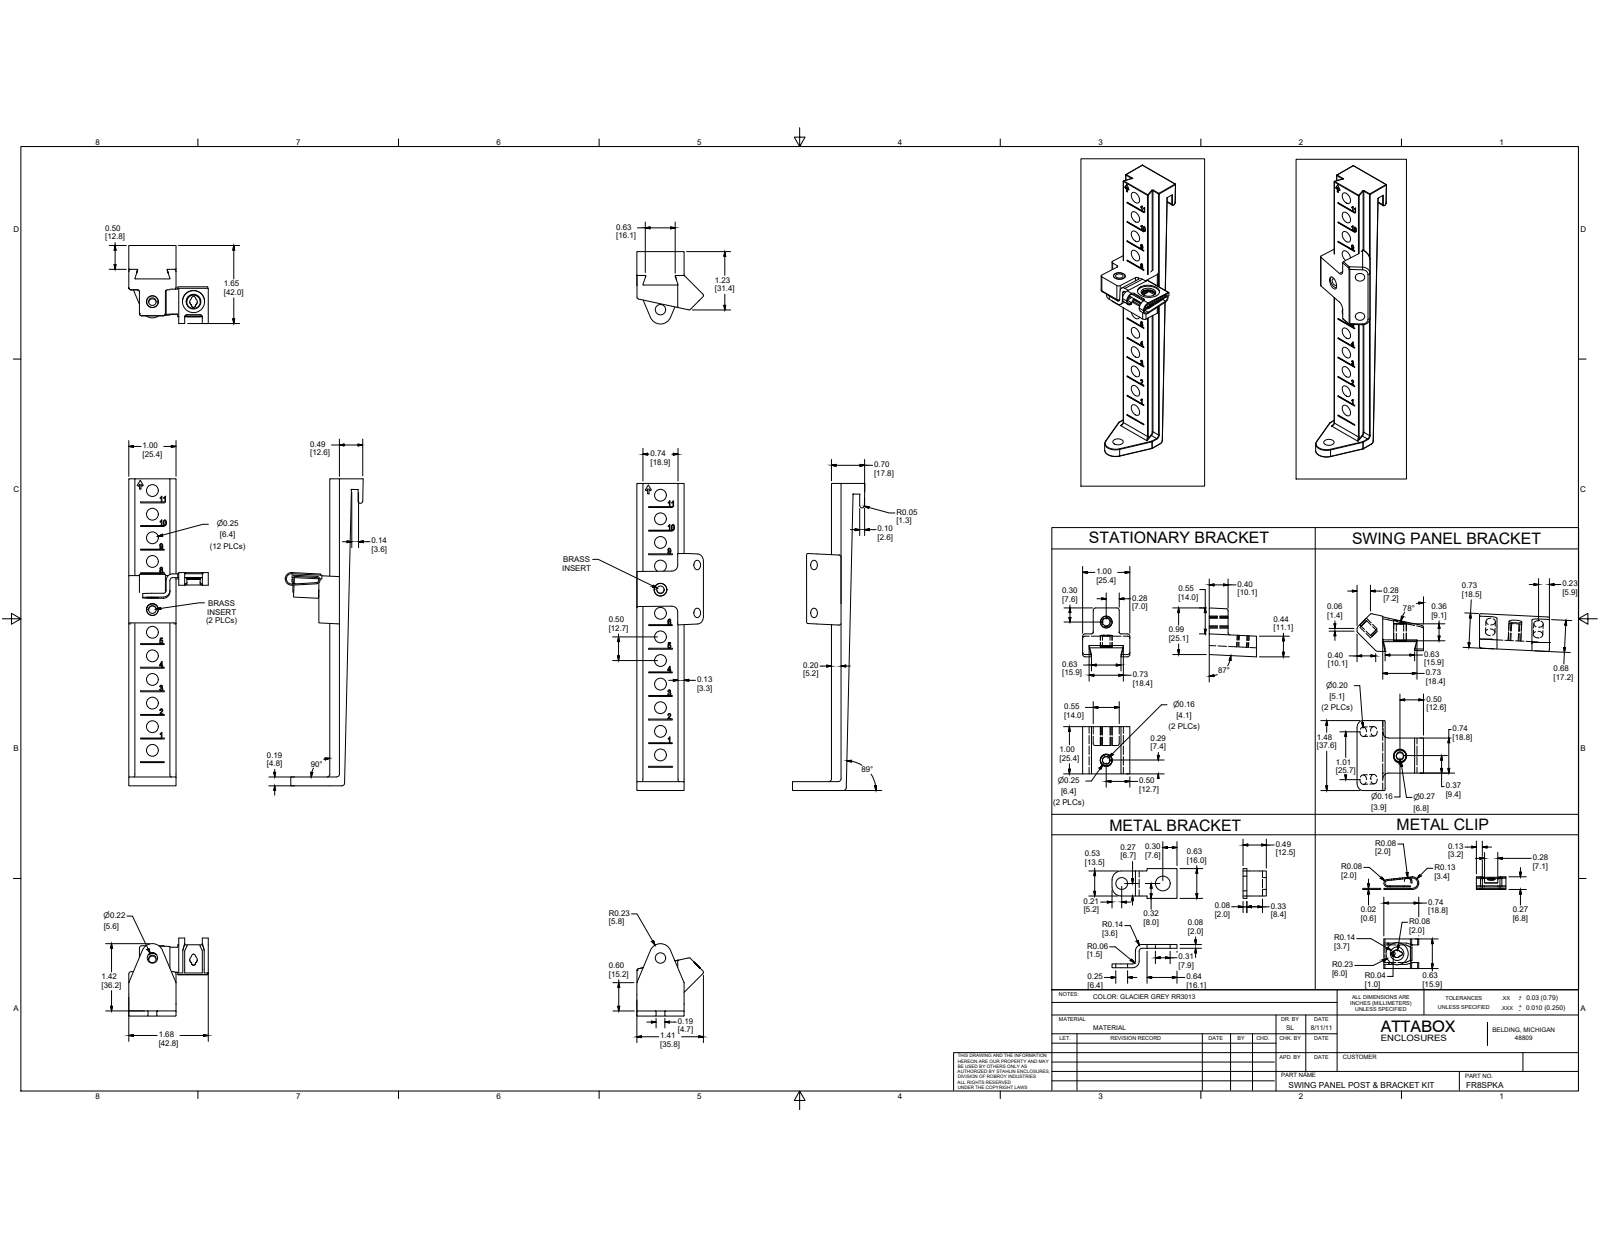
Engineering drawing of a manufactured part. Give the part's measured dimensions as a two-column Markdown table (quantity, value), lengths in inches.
| quantity | value |
| --- | --- |
| part name | FR8SPKA |
| STEP written by | SolidWorks 2019 (AUTOMOTIVE_DESIGN) |
| units | inches |
| bodies | 32 solids, 1984 faces (976 planar, 418 cylindrical, 590 other) |
| overall size | 14.688 × 12.688 × 6.728 |
| volume | 11.2 in³ |
| surface area | 144.5 in² |
| round holes (diameter × count) | 0.25 × 50, 0.156 × 6, 0.253 × 6, 0.217 × 4, 0.22 × 4, 0.312 × 3, 0.35 × 2 |
| round bosses / shafts (diameter × count) | 0.19 × 10, 0.373 × 6, 0.246 × 6, 0.433 × 4, 0.315 × 4 |
| partial cylindrical surfaces (radius × count) | 0.01 × 204, 0.06 × 44, 0.063 × 14, 0.025 × 8, 0.13 × 6, 0.049 × 4, 0.062 × 4, 0.19 × 4 |
| main face-to-face distances | 16.951, 0.203, 17.154, 1, 1.414, 8.472, 8.886, 8.269, 8.683, 7.472 |
| hole center spacings | 1.5, 0.5, 1, 1.732, 2.061, 2, 2.45, 2.5 |
